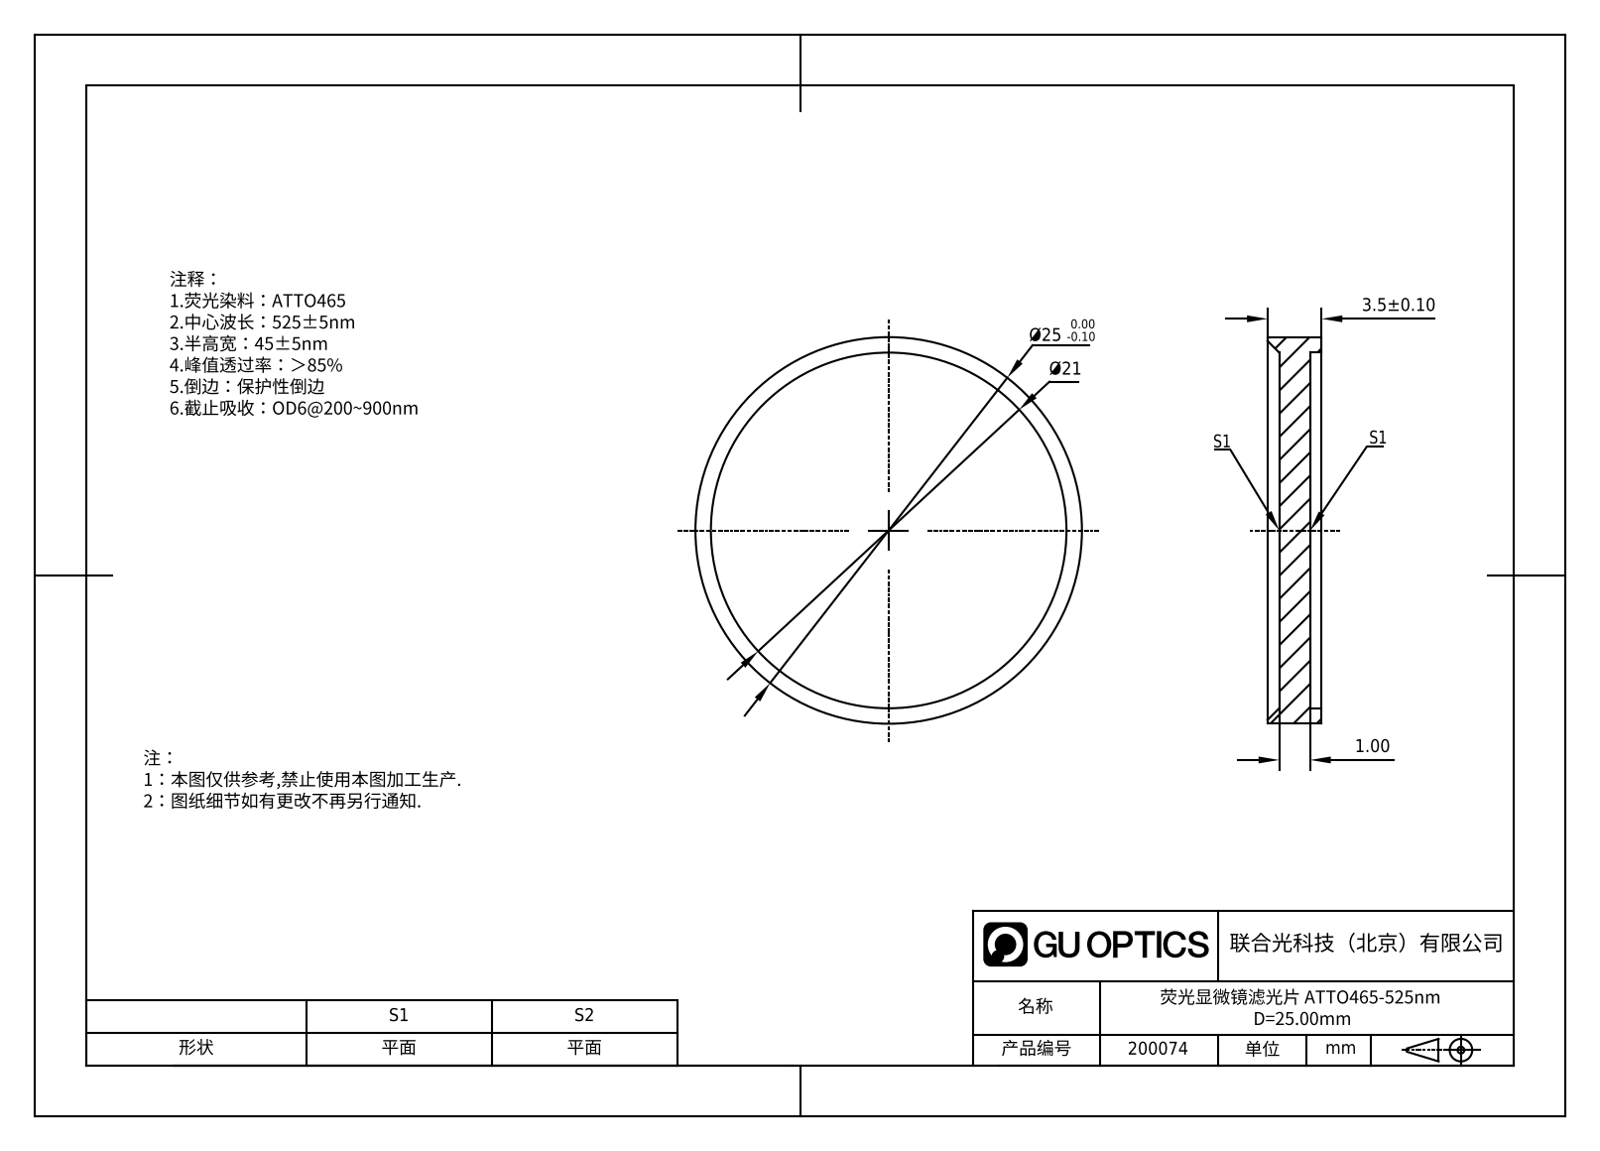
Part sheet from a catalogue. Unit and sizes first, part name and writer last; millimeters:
Units: millimetres
Overall size (bounding box): 25 × 25 × 3.5
Round holes (diameter × count): ⌀23 ×1
Round bosses / shafts (diameter × count): ⌀25 ×1
Main face-to-face distances: 2, 0.75, 2.75, 3.5
Volume: 1 074 mm³ · Surface area: 1 334 mm²
Bodies: 1 solid, 10 faces (4 planar, 4 cylindrical, 2 other)
Part name (STEP PRODUCT): GNIF-045-525-D25
STEP written by: SolidWorks 2022 (AUTOMOTIVE_DESIGN)
